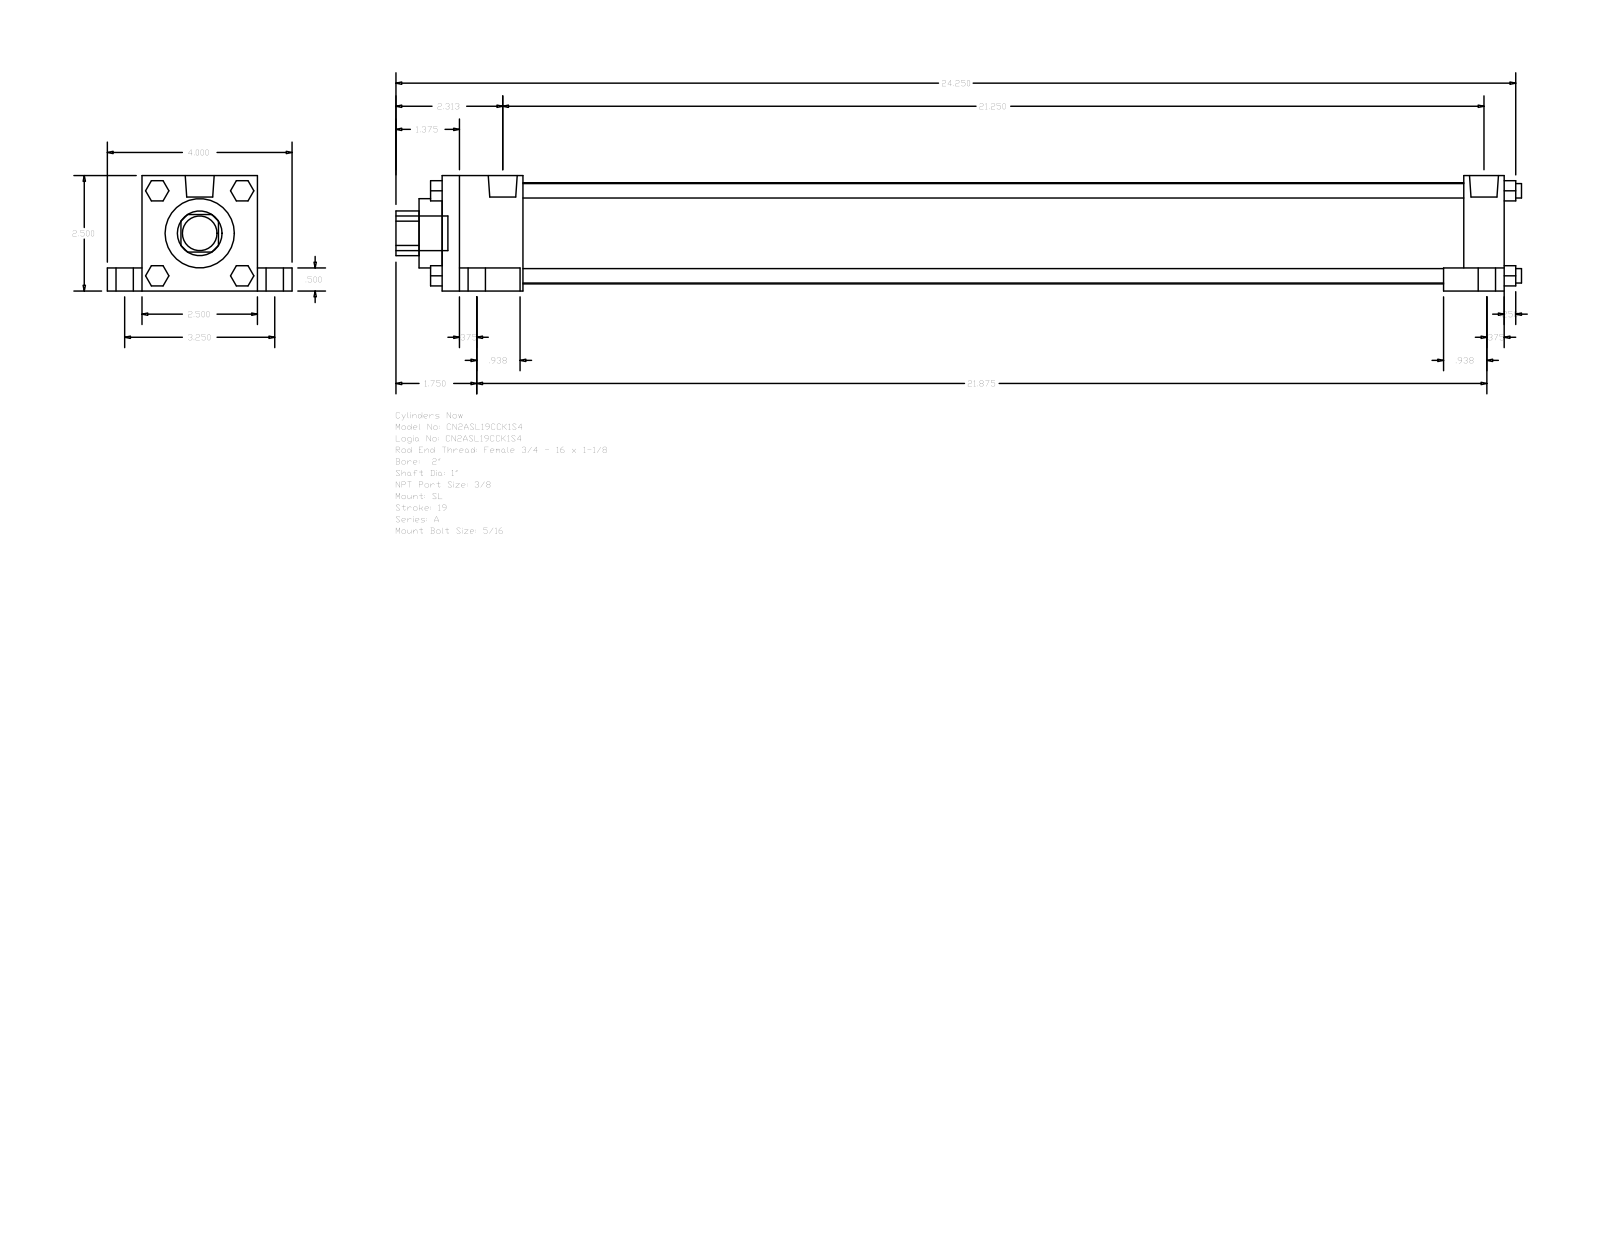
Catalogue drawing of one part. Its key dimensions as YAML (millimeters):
part_name: "A_SL__0200_1"
step_written_by: "GSSL Pune (CONFIG_CONTROL_DESIGN)"
units: millimeters
bodies: {solids: 0, faces: 148, planar: 112, cylindrical: 36, other: 0}
overall_size: [619.12, 101.6, 63.5]
round_holes:
  - {diameter: 25.4, count: 1}
  - {diameter: 38.1, count: 1}
  - {diameter: 55.63, count: 1}
round_bosses_or_shafts:
  - {diameter: 15.88, count: 4}
  - {diameter: 9.53, count: 4}
  - {diameter: 7.94, count: 4}
  - {diameter: 5.56, count: 4}
  - {diameter: 15.93, count: 2}
  - {diameter: 19.05, count: 1}
partial_cylinders:
  - {radius: 12.29, count: 1}
face_to_face_distances: [63.5, 584.2, 12.7, 50.8, 22.22, 19.05, 82.55, 9.52, 44.45, 539.75]
